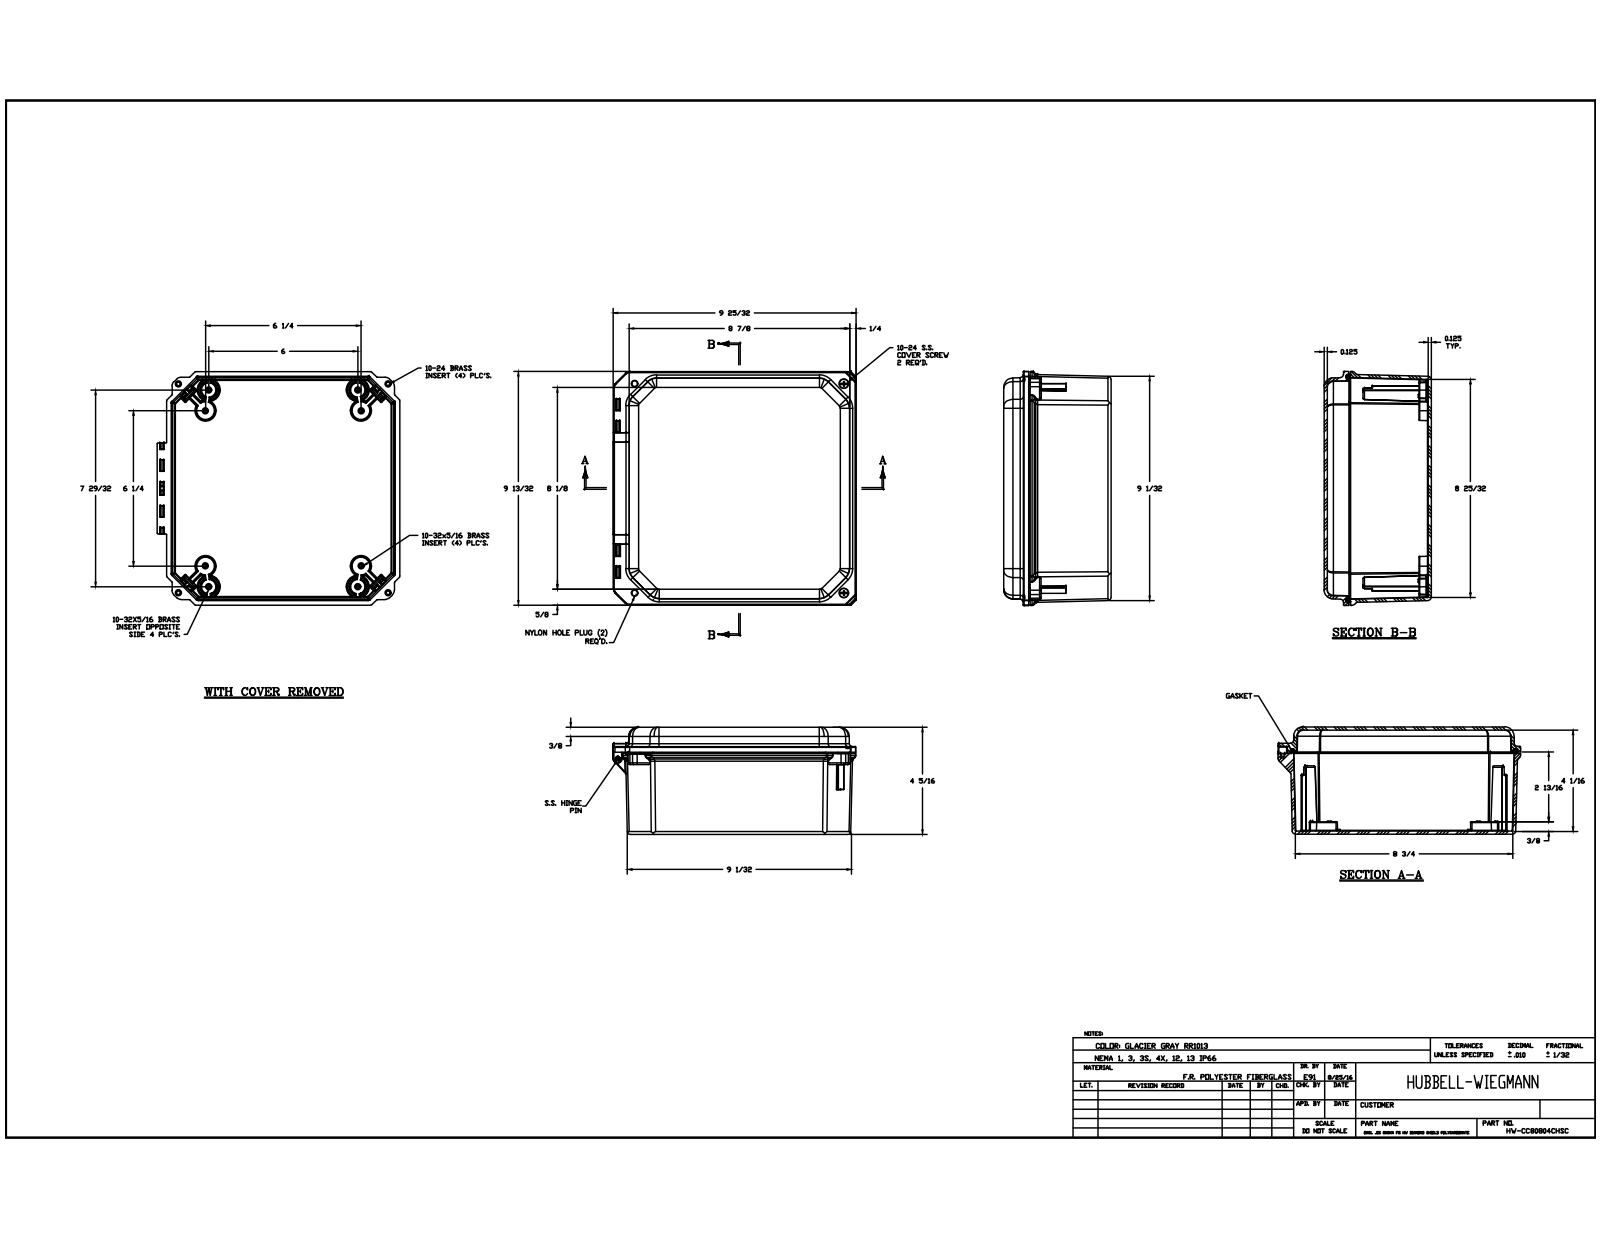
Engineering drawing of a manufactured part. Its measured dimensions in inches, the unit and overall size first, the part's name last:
Units: inches
Overall size (bounding box): 9.767 × 9.39 × 4.312
Round holes (diameter × count): ⌀0.156 ×12, ⌀0.152 ×8, ⌀0.219 ×4, ⌀0.252 ×4, ⌀0.312 ×4, ⌀0.15 ×2, ⌀0.137 ×1
Round bosses / shafts (diameter × count): ⌀0.246 ×12, ⌀0.87 ×4, ⌀0.45 ×2, ⌀0.209 ×2, ⌀0.199 ×2, ⌀0.135 ×1
Partial cylindrical surfaces — rounded edges, fillets, slot ends (radius × count): R0.01 ×140, R0.005 ×94, R0.02 ×67, R0.03 ×37, R0.125 ×29, R0.03 ×24, R0.09 ×24, R0.25 ×24
Main face-to-face distances: 0.125, 4.187, 4.312, 4.062, 0.124, 3.531, 0.656, 0.875, 3.312, 3.187
Hole centre spacings: 6.181, 6.25, 7.41, 7.411, 1.232, 1.53, 7.21, 8.414
Volume: 44.61 in³ · Surface area: 686 in²
Bodies: 23 solids, 1955 faces (536 planar, 717 cylindrical, 702 other)
Part name (STEP PRODUCT): HW-CC80804CHSC; DS080804BOX; BRASS INSERT-(; BRASS INSERT-(_1 (+7 more)
STEP written by: Autodesk Inventor 2017 (CONFIG_CONTROL_DESIGN)
